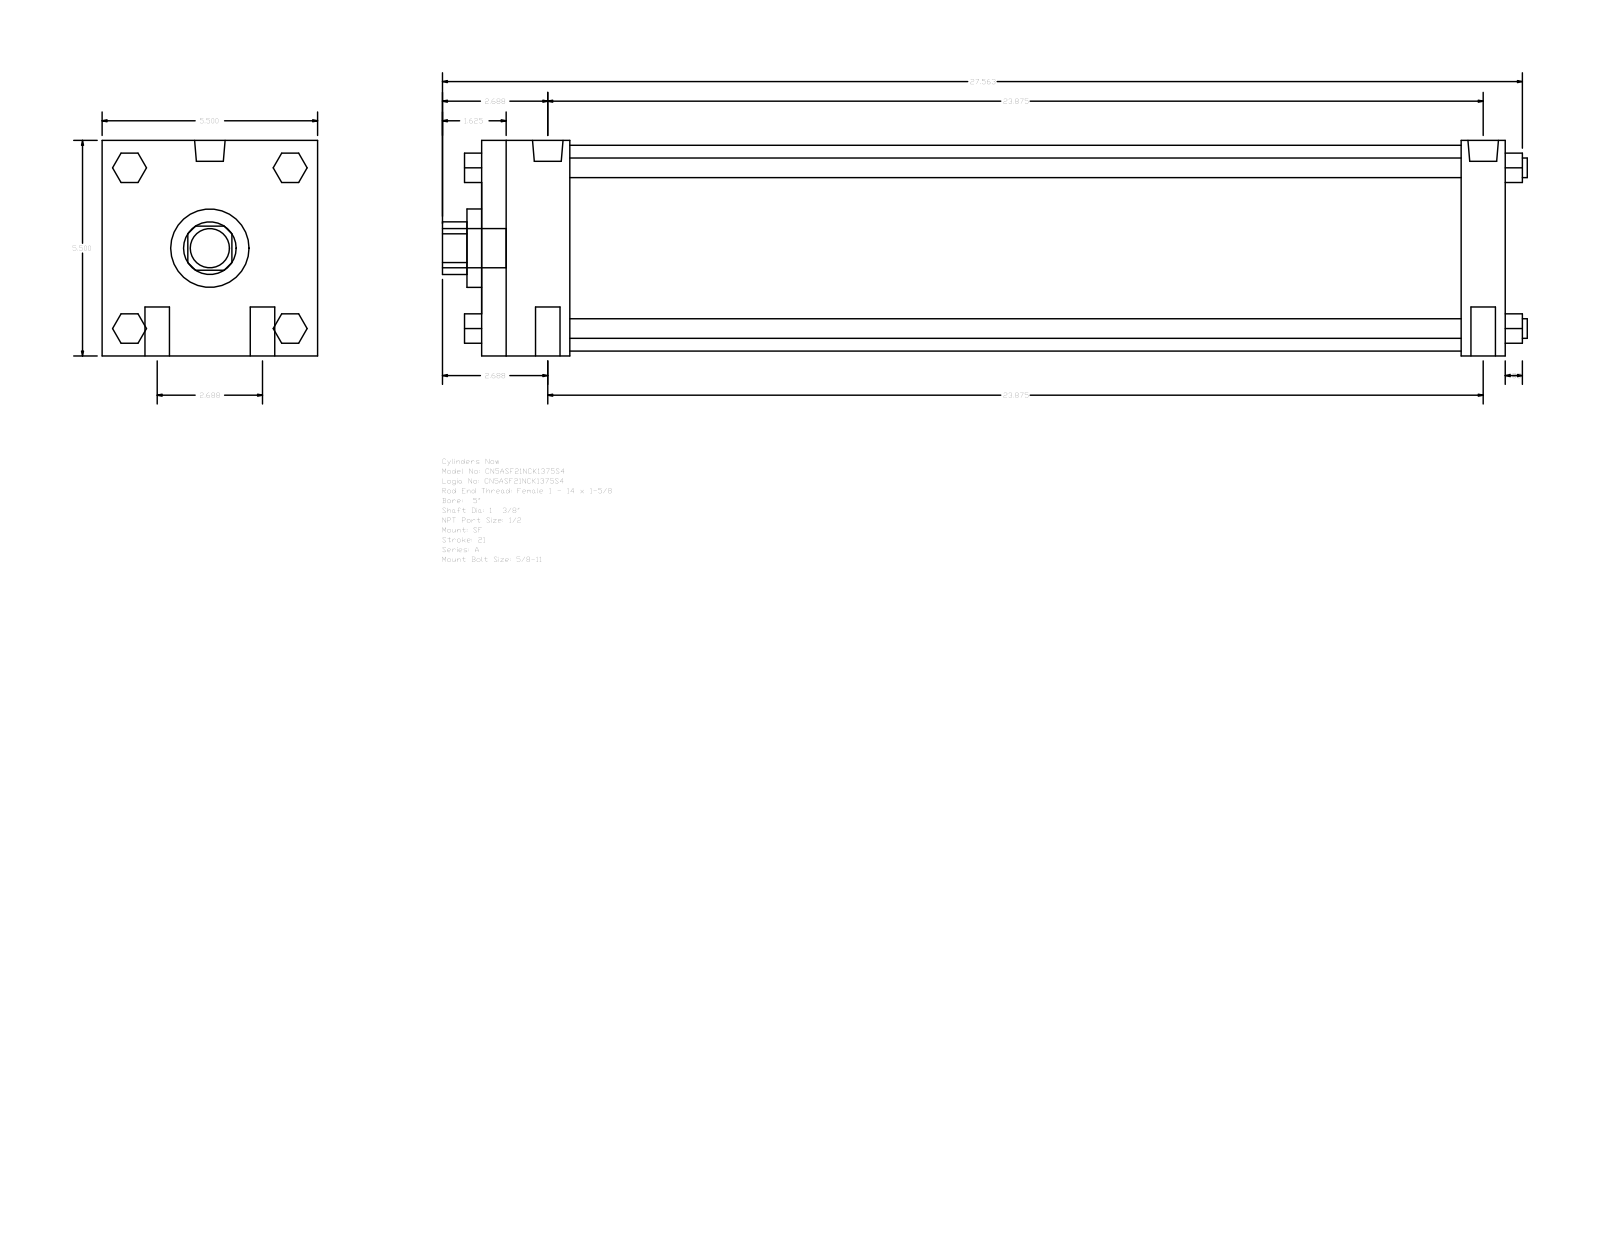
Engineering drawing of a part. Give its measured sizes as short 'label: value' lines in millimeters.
name: A_SF__0500_1.375
written by: GSSL Pune (CONFIG_CONTROL_DESIGN)
unit: mm
bodies: 0 solids, 124 faces (94 planar, 30 cylindrical, 0 other)
size: 703.26 × 139.7 × 139.7
holes: 1× ⌀34.92, 1× ⌀50.8, 1× ⌀133.35
bosses: 4× ⌀15.88, 4× ⌀12.7, 2× ⌀19.77, 2× ⌀8.73, 1× ⌀25.4
rounds: 1× R17.06
face distances: 139.7, 663.58, 28.58, 57.15, 635, 577.85, 606.43, 19.05, 52.07, 90.18
